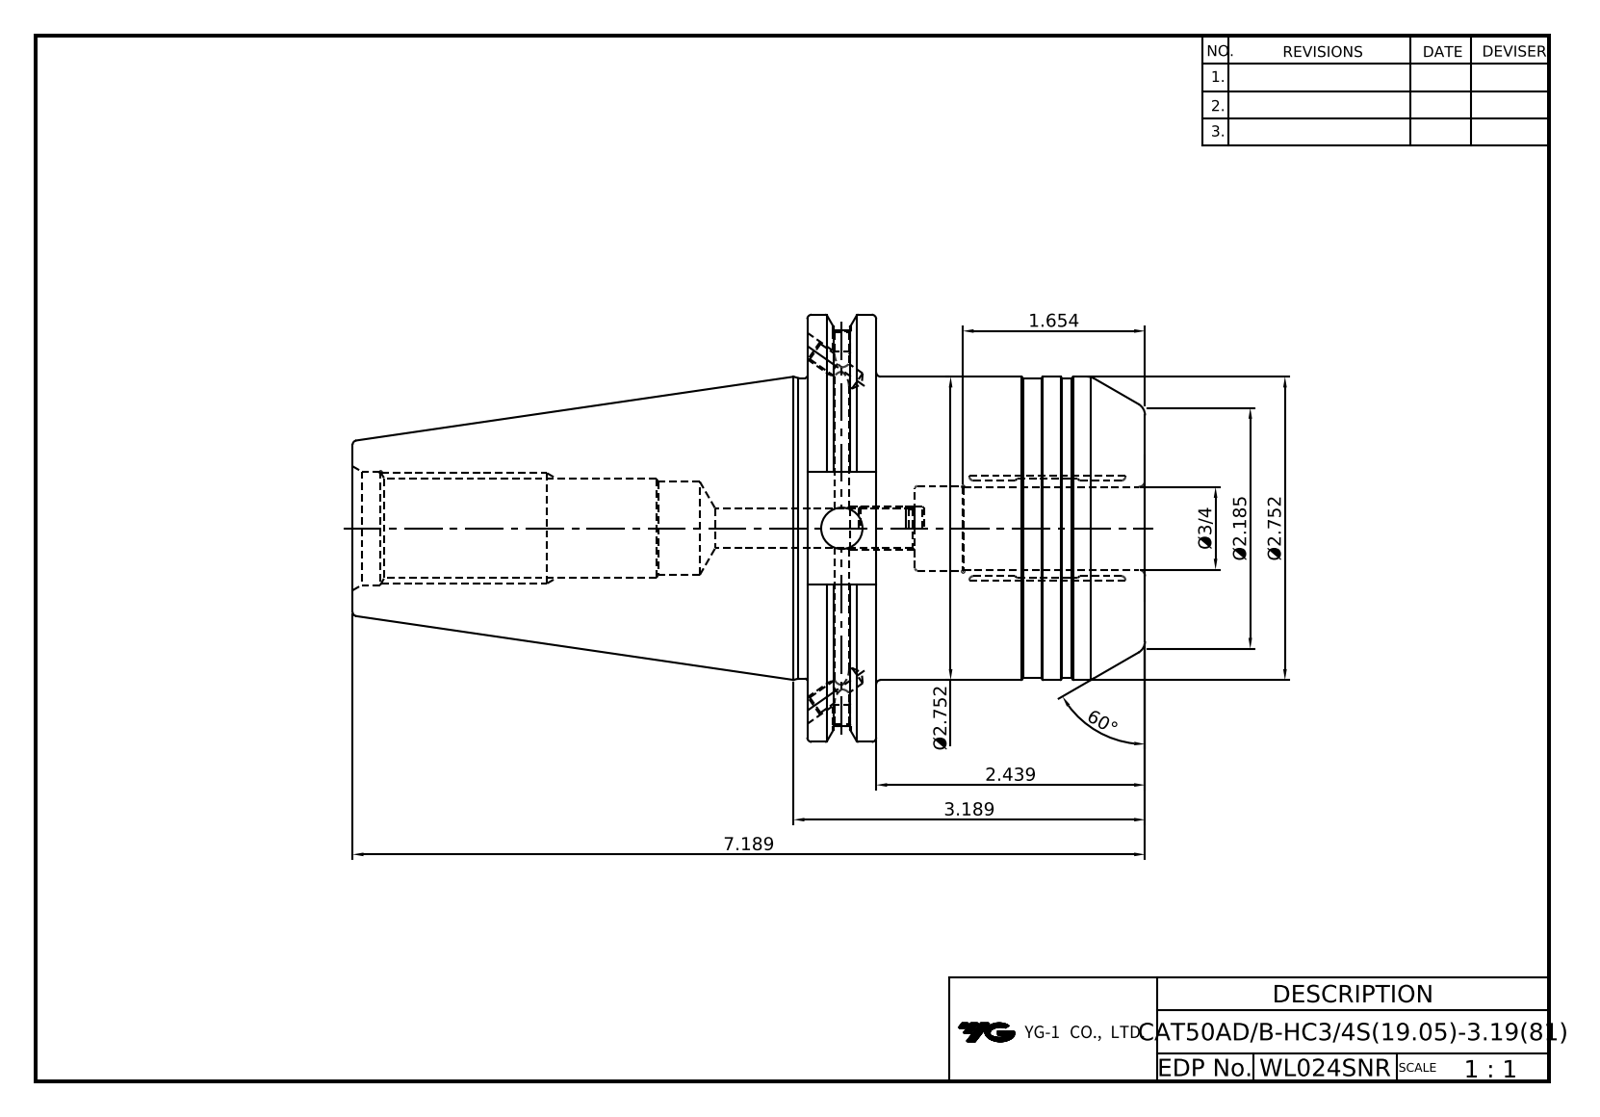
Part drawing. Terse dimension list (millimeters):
name: LO-CAT50ADB-HC19.05S-81
written by: Autodesk Inventor 2025 (AUTOMOTIVE_DESIGN)
unit: mm
bodies: 1 solid, 102 faces (37 planar, 31 cylindrical, 34 other)
size: 182.6 × 98.42 × 94.69
volume: 542 362 mm³; area: 59 448 mm²
holes: 2× ⌀3.24, 2× ⌀4.13, 2× ⌀4.2, 2× ⌀5, 1× ⌀8.92, 1× ⌀9.53, 1× ⌀19.05, 1× ⌀19.4, 1× ⌀21.5, 1× ⌀21.97, 1× ⌀26.2
bosses: 1× ⌀98.42, 1× ⌀91.29, 1× ⌀69.9, 1× ⌀69.25, 1× ⌀68.9
face distances: 15.88, 77.83, 61.95, 104.77, 120.65, 182.6, 73.03, 25.9, 129.6, 24.83
